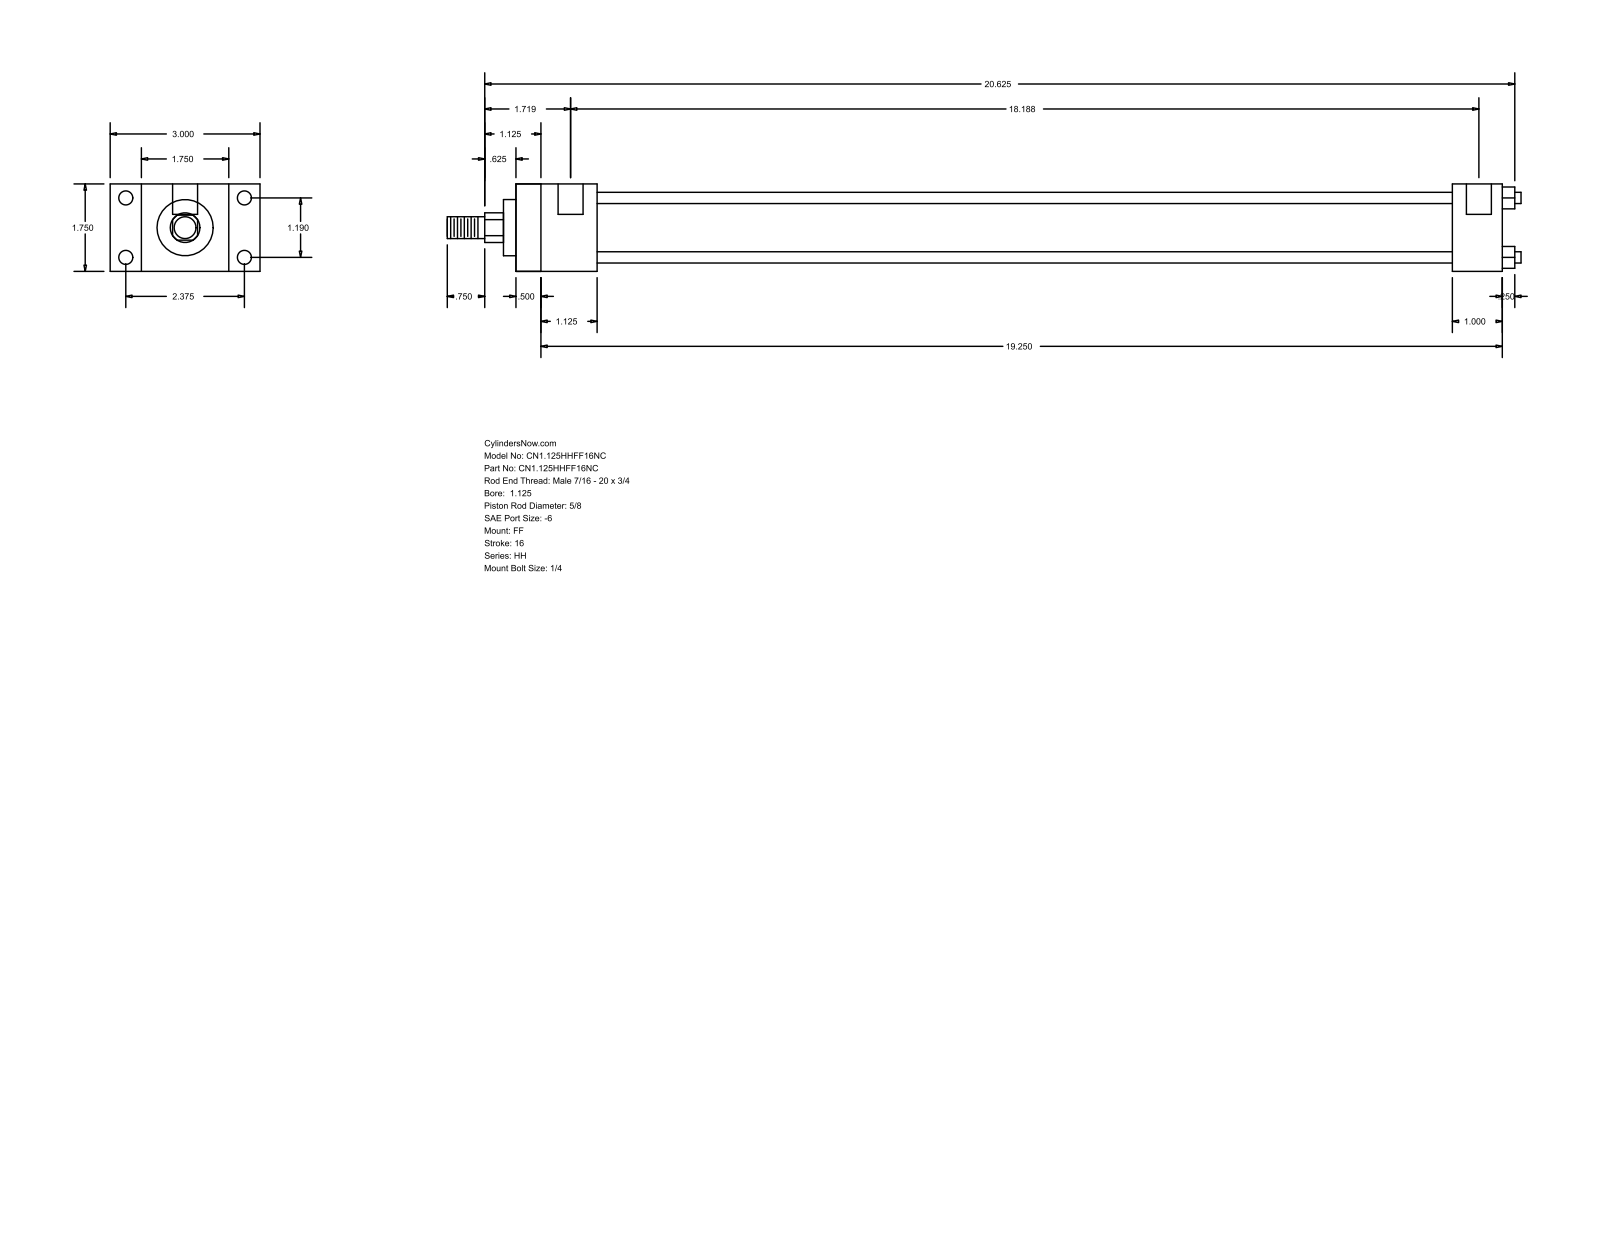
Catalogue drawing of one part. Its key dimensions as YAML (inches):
part_name: "HH_FF__0112_0.625"
step_written_by: "GSSL Pune (CONFIG_CONTROL_DESIGN)"
units: inches
bodies: {solids: 0, faces: 92, planar: 64, cylindrical: 28, other: 0}
overall_size: [21.5, 3, 1.75]
round_holes:
  - {diameter: 0.219, count: 4}
  - {diameter: 0.281, count: 4}
  - {diameter: 0.5, count: 2}
round_bosses_or_shafts:
  - {diameter: 0.225, count: 4}
  - {diameter: 1.375, count: 1}
  - {diameter: 1.125, count: 1}
  - {diameter: 0.625, count: 1}
  - {diameter: 0.437, count: 1}
partial_cylinders:
  - {radius: 0.297, count: 1}
face_to_face_distances: [1.75, 19.75, 0.625, 0.5, 19.25, 1.125, 2.375, 1, 1.625, 18.75]
hole_center_spacings: [1.19, 2.375, 2.656, 18.063, 0.125, 18.187]
